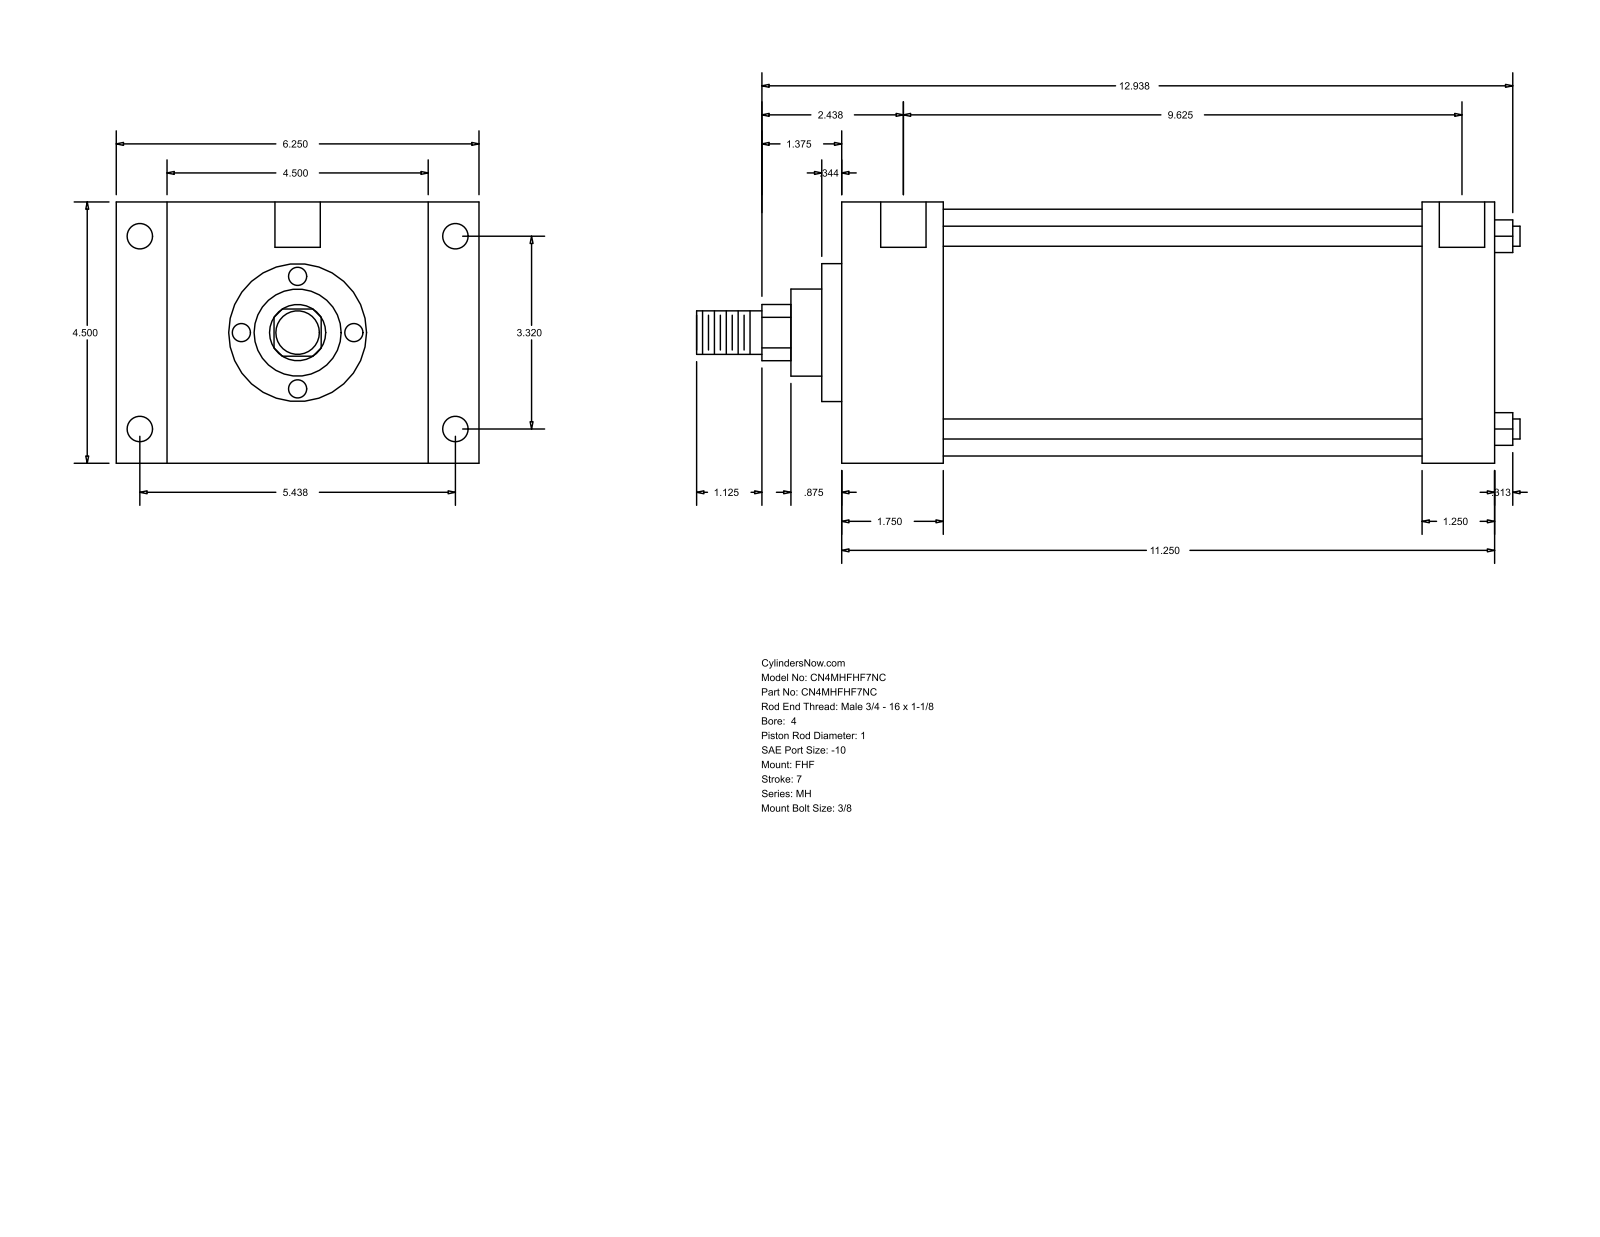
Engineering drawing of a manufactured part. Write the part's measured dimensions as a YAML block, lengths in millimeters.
part_name: "MH_FHF__0400_1"
step_written_by: "GSSL Pune (CONFIG_CONTROL_DESIGN)"
units: millimeters
bodies: {solids: 0, faces: 90, planar: 61, cylindrical: 29, other: 0}
overall_size: [360.36, 158.75, 114.3]
round_holes:
  - {diameter: 8.73, count: 4}
  - {diameter: 11.13, count: 4}
  - {diameter: 19.84, count: 2}
round_bosses_or_shafts:
  - {diameter: 8.76, count: 4}
  - {diameter: 107.95, count: 1}
  - {diameter: 60.33, count: 1}
  - {diameter: 38.1, count: 1}
  - {diameter: 25.4, count: 1}
  - {diameter: 19.05, count: 1}
partial_cylinders:
  - {radius: 12.29, count: 1}
face_to_face_distances: [114.3, 285.76, 44.46, 241.3, 22.23, 136.53, 158.76, 254.01, 209.55, 31.75]
hole_center_spacings: [84.32, 138.12, 161.82, 247.65, 1.58, 1.59, 244.48, 246.06]
